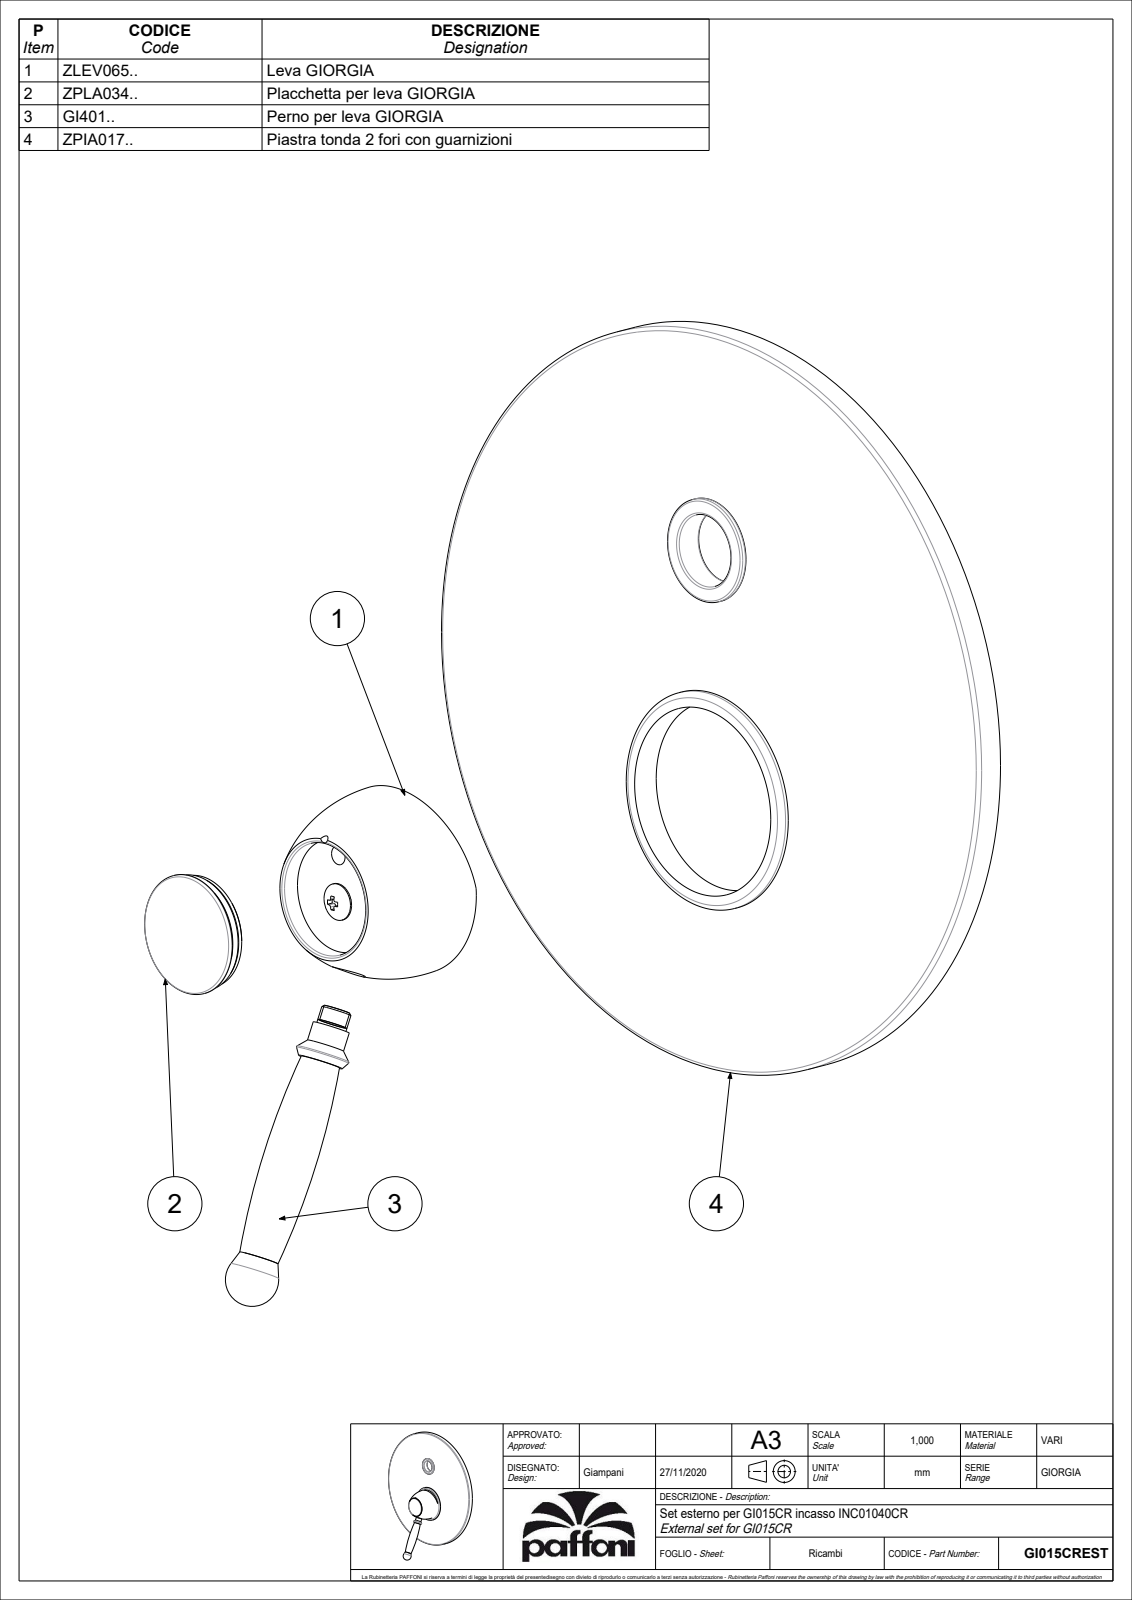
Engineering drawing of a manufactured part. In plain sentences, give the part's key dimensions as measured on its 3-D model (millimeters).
The part is named "GI015CREST". Its 3-D file was written by "CREO PARAMETRIC BY PTC INC, 2020044 (CONFIG_CONTROL_DESIGN)". It is 1 solid with 238 faces: 119 planar, 54 cylindrical and 65 other. Overall it measures 218.4 by 200 by 69.37 millimeters. Its volume is 175 211 cubic millimeters and its surface area 96 183 square millimeters. Round holes: 2 of diameter 5, 1 of diameter 12, 1 of diameter 19.1, 1 of diameter 30.3, 1 of diameter 50.5, 1 of diameter 145, 1 of diameter 198. Round bosses or shafts: 1 of diameter 200, 1 of diameter 195, 1 of diameter 58.5, 1 of diameter 54, 1 of diameter 32, 1 of diameter 29.9, 1 of diameter 27, 1 of diameter 25.1. Partial cylindrical surfaces (rounded edges, fillets, slot ends): 4 of radius 0.5, 1 of radius 2, 1 of radius 3.5, 1 of radius 24.35. The main face-to-face distances are 1, 8, 9, 31, 32, 36.7, 28.7, 27.7, 7, 35.7. The hole center spacings are 1.6, 11, 12.6, 15.75, 26.75, 28.35, 41.25, 57.
